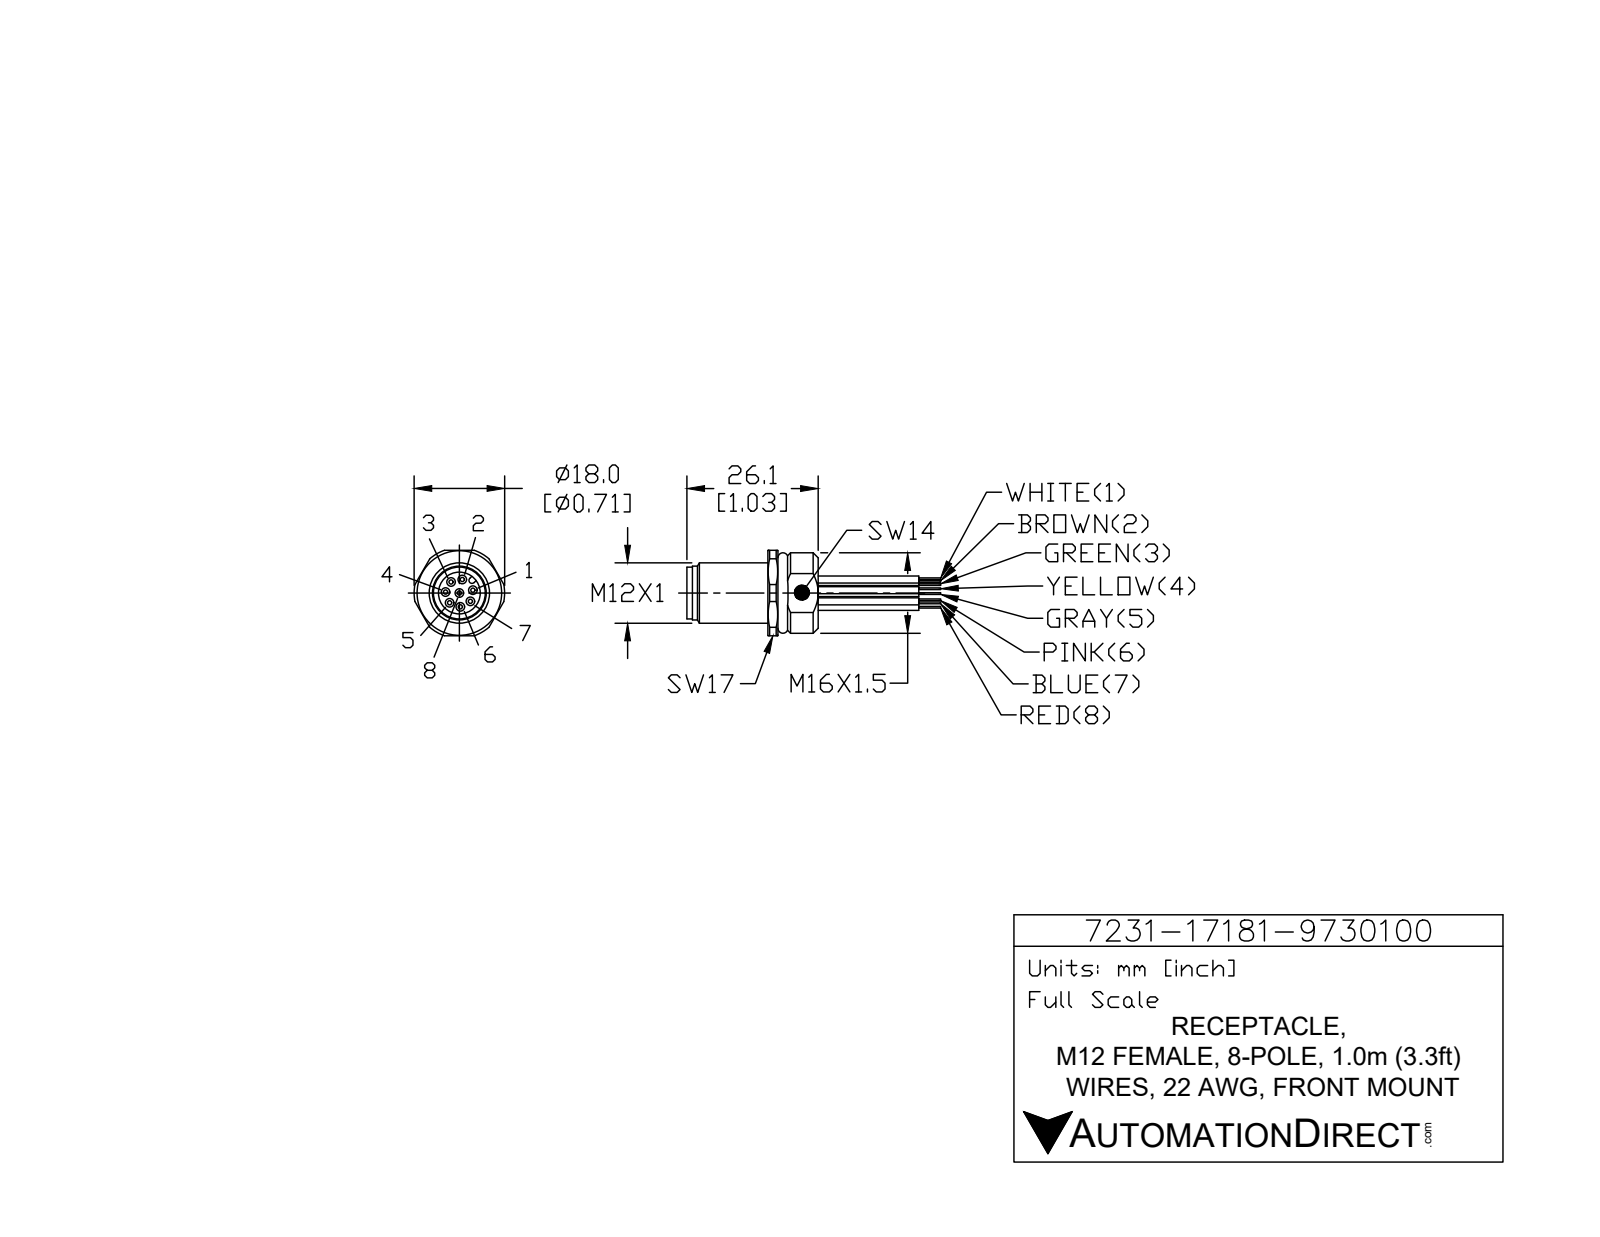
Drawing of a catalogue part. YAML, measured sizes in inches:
part_name: "7231-17181-9730100"
step_written_by: "SolidWorks 2015 (AUTOMOTIVE_DESIGN)"
units: inches
bodies: {solids: 1, faces: 145, planar: 35, cylindrical: 53, other: 57}
overall_size: [1.677, 0.709, 0.669]
volume: 0.208
surface_area: 4.644
round_holes:
  - {diameter: 0.035, count: 8}
  - {diameter: 0.43, count: 1}
  - {diameter: 0.48, count: 1}
  - {diameter: 0.512, count: 1}
round_bosses_or_shafts:
  - {diameter: 0.055, count: 8}
  - {diameter: 0.531, count: 1}
  - {diameter: 0.319, count: 1}
partial_cylinders:
  - {radius: 0.026, count: 1}
  - {radius: 0.315, count: 1}
  - {radius: 0.354, count: 1}
face_to_face_distances: [0.354, 0.496, 0.276, 0.079, 0.22, 0.142, 0.551, 0.85, 0.575, 0.669]
hole_center_spacings: [0.108, 0.163, 0.207, 0.214, 0.089, 0.09, 0.09, 0.183]
